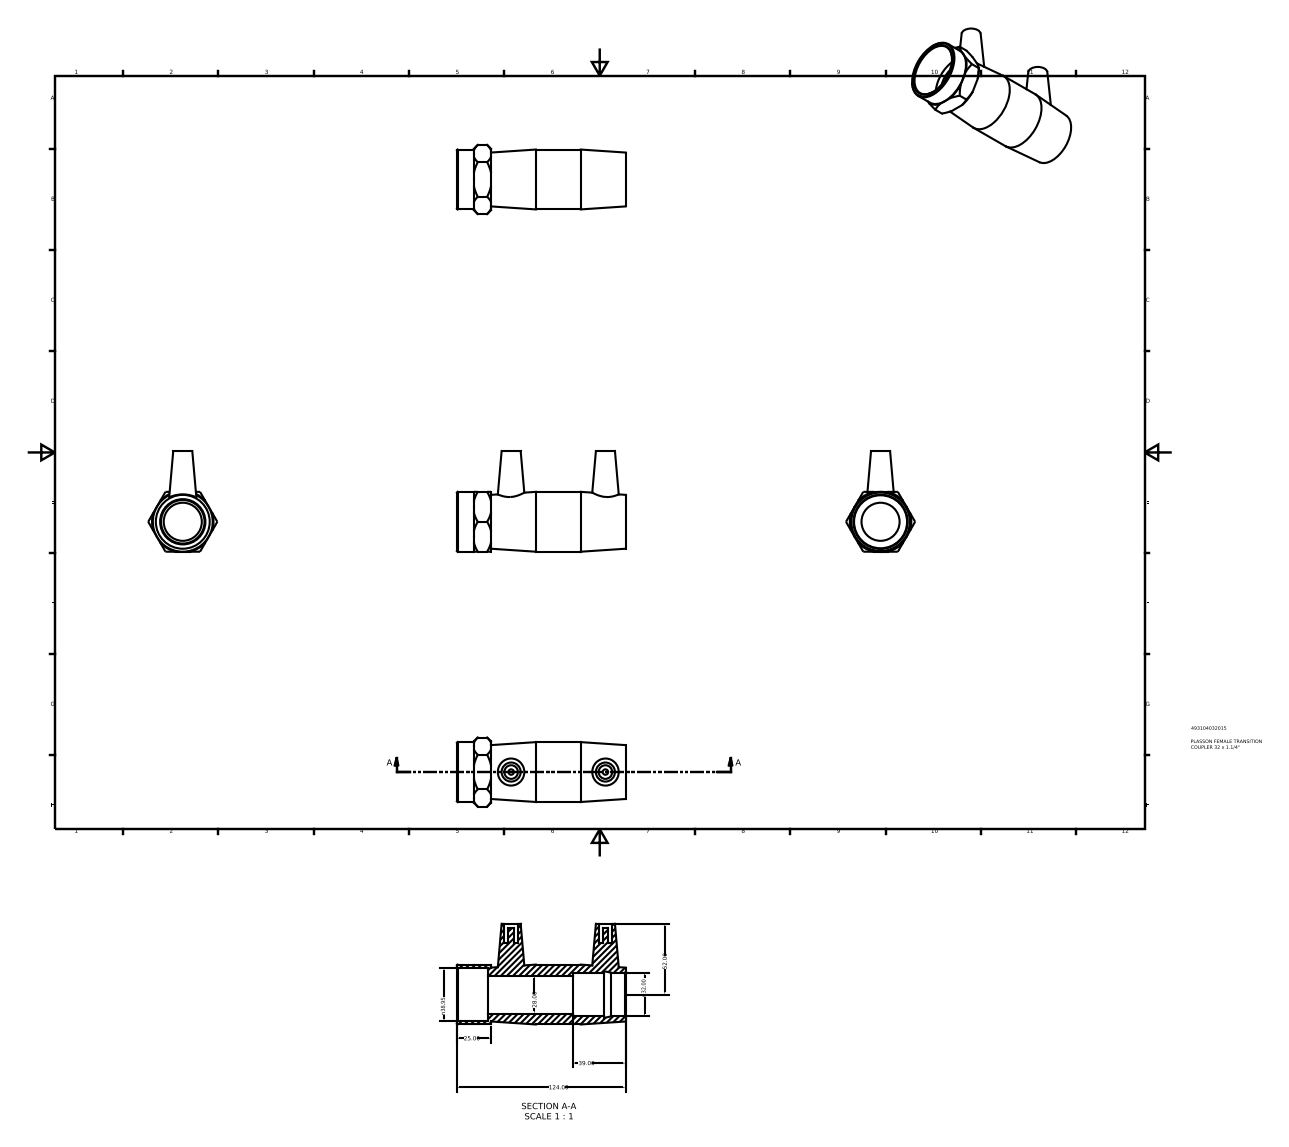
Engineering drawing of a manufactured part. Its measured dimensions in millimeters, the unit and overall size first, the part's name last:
Units: millimetres
Overall size (bounding box): 124 × 74 × 50.81
Round holes (diameter × count): ⌀10 ×2, ⌀28 ×1, ⌀32 ×1, ⌀38.95 ×1
Round bosses / shafts (diameter × count): ⌀4 ×2, ⌀44 ×1
Main face-to-face distances: 44, 101.5, 2.5, 99, 60, 22.5, 25, 124, 85, 62.5
Hole centre spacings: 69.3
Volume: 95 901 mm³ · Surface area: 35 349 mm²
Bodies: 1 solid, 54 faces (24 planar, 10 cylindrical, 20 other)
Part name (STEP PRODUCT): 493104032015
STEP written by: Autodesk Inventor 2015 (AUTOMOTIVE_DESIGN)
